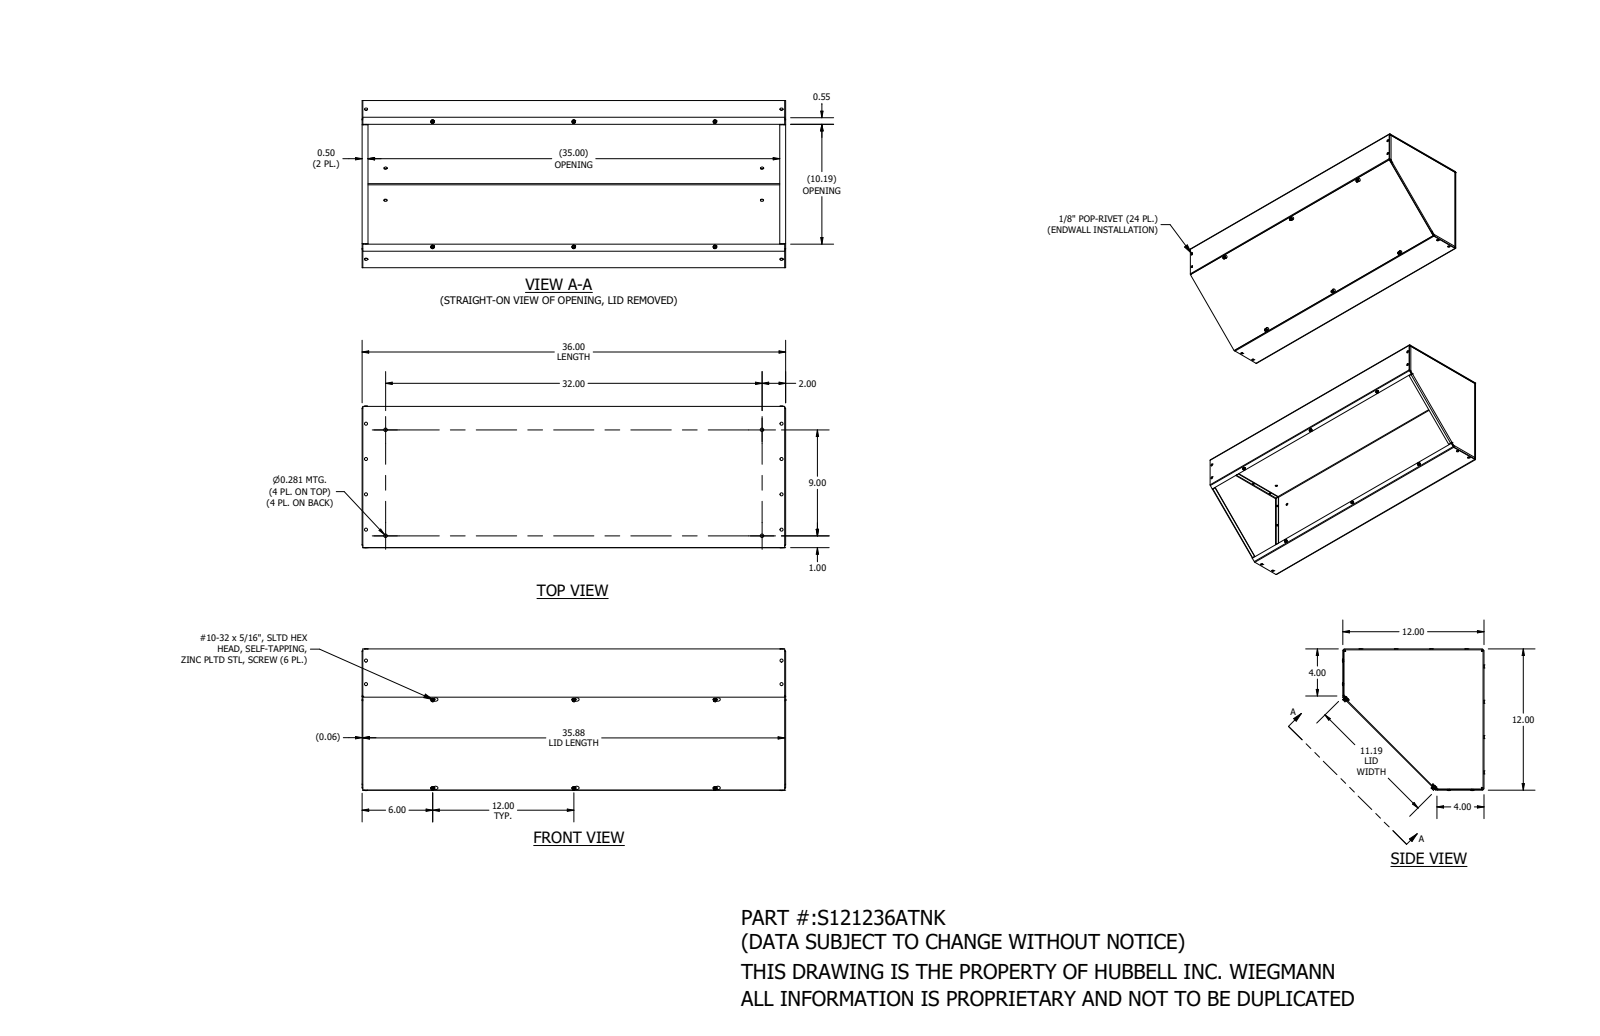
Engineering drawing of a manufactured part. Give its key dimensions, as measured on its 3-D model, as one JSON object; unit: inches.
{"part_name": "S121236ATNK", "step_written_by": "SolidWorks 2021 (AUTOMOTIVE_DESIGN)", "units": "inches", "bodies": {"solids": 34, "faces": 1504, "planar": 362, "cylindrical": 442, "other": 700}, "overall_size": [36, 12.08, 12.08], "volume_in3": 135, "surface_area_in2": 3681, "round_holes": [[0.129, 24], [0.281, 8], [0.171, 6], [0.406, 6]], "round_bosses_or_shafts": [[0.262, 24], [0.125, 18], [0.313, 6], [0.181, 6], [0.125, 6]], "partial_cylinders_radius": [[0.064, 48], [0.136, 15], [0.063, 13], [0.109, 6], [0.062, 2]], "face_to_face_distances": [0.074, 11.926, 11.852, 12, 35.926, 36, 35.852, 0.067, 0.141, 0.148], "hole_center_spacings": [3, 35.313, 35.44, 1.5, 1.735, 6, 9, 12]}
